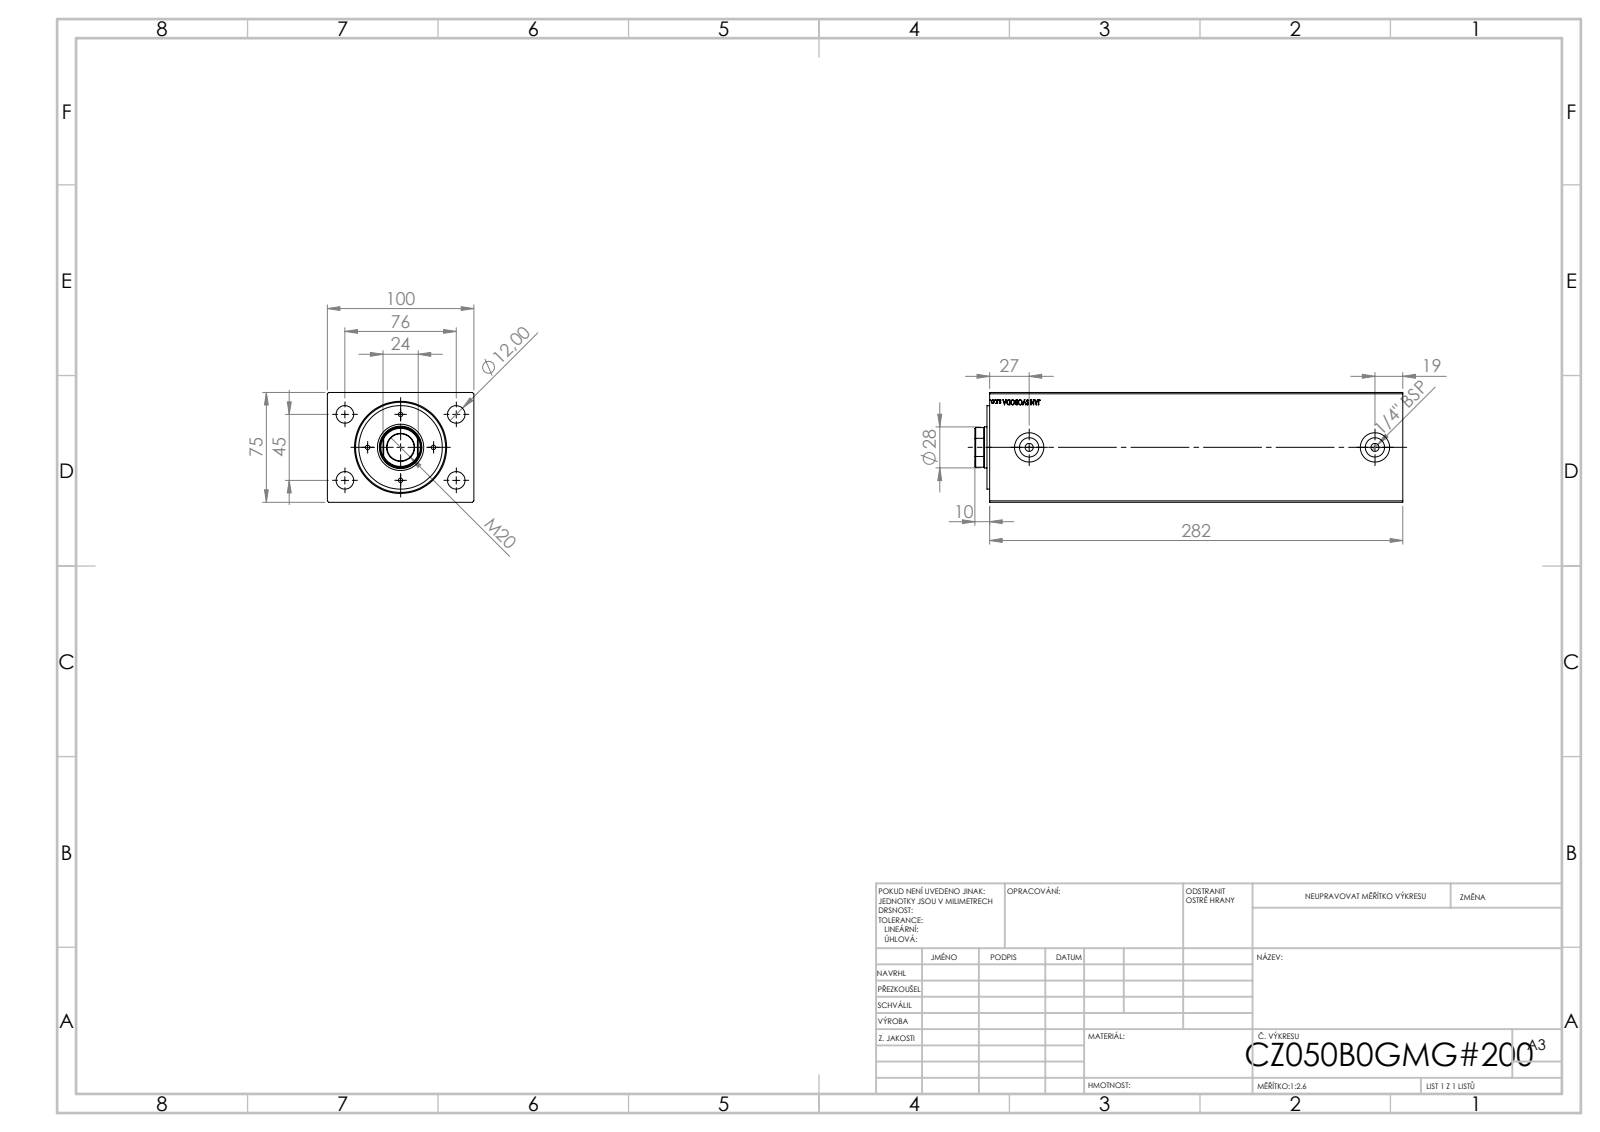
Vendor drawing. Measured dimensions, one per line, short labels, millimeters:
name: V500CZ; V500CZ_B_VC
written by: SolidWorks 2019 (CONFIG_CONTROL_DESIGN)
unit: mm
bodies: 3 solids, 873 faces (399 planar, 58 cylindrical, 416 other)
size: 292 × 100 × 75
volume: 1 887 000 mm³; area: 226 655 mm²
holes: 4× ⌀3, 4× ⌀12, 2× ⌀5.5, 2× ⌀13.16, 2× ⌀20, 1× ⌀18.5, 1× ⌀28, 1× ⌀29, 1× ⌀36, 1× ⌀50, 1× ⌀61.5
bosses: 1× ⌀57
rounds: 1× R13.5
face distances: 75, 100, 282, 264.5, 17.5, 82, 182.5, 200, 1.8, 83.8
hole spacings: 22.5, 27.32, 31.82, 38, 44.16, 45, 58.9, 64.55
